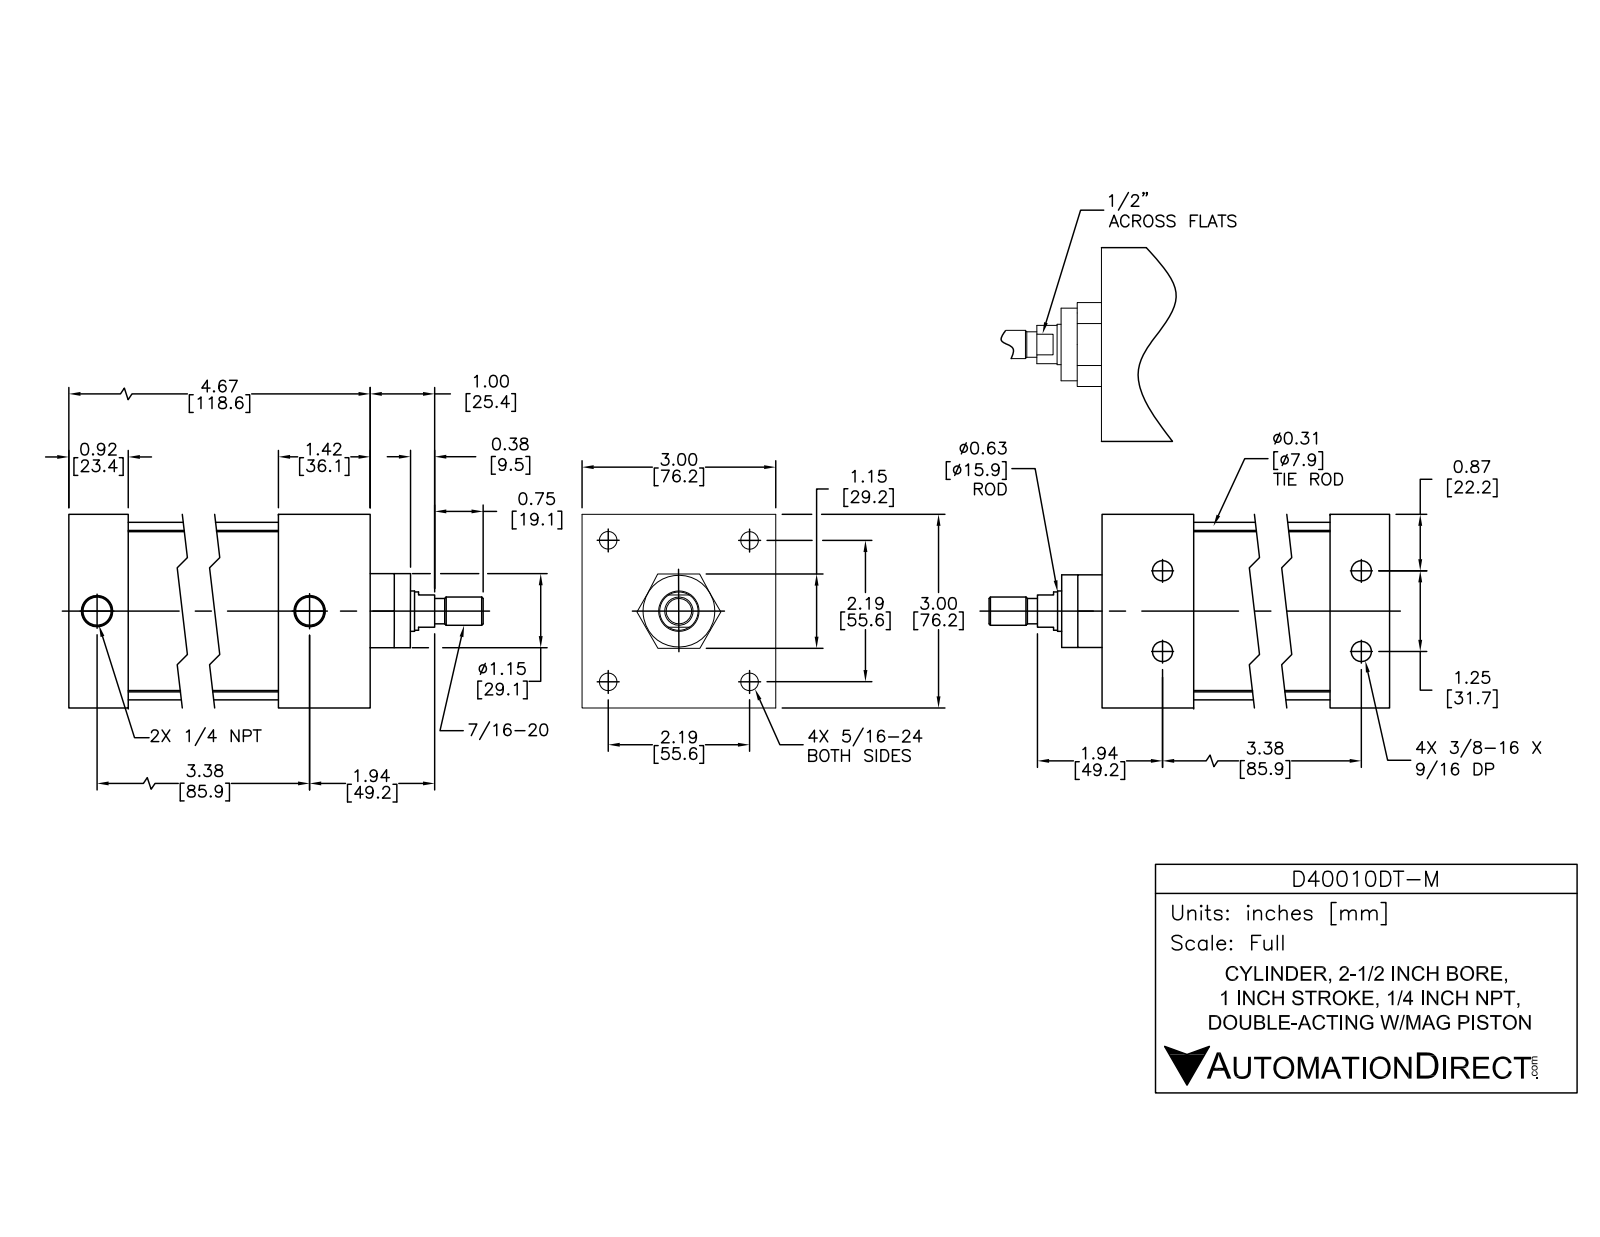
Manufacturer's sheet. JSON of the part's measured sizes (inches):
{"part_name": "D40010DT-M BODY; D40010DT-M PISTON; D40010DT-M", "step_written_by": "SolidWorks 2015 (AUTOMOTIVE_DESIGN)", "units": "inches", "bodies": {"solids": 12, "faces": 298, "planar": 94, "cylindrical": 114, "other": 90}, "overall_size": [6.496, 3, 3], "volume_in3": 30.8, "surface_area_in2": 174.7, "round_holes": [[0.267, 4], [0.307, 4], [0.359, 4], [0.5, 4], [0.297, 2], [0.477, 2], [0.625, 1], [0.628, 1], [2.5, 1]], "round_bosses_or_shafts": [[0.484, 4], [0.313, 4], [0.282, 4], [2.75, 1], [2.497, 1], [1.12, 1], [0.622, 1], [0.59, 1]], "partial_cylinders_radius": [[0.3, 4]], "face_to_face_distances": [3, 4.746, 3.726, 1.02, 1.42, 2.306, 3.326, 1, 3.826, 2.406], "hole_center_spacings": [1.556, 2.2, 3.428, 3.37, 0.625, 0.625, 1.25, 3.111]}
